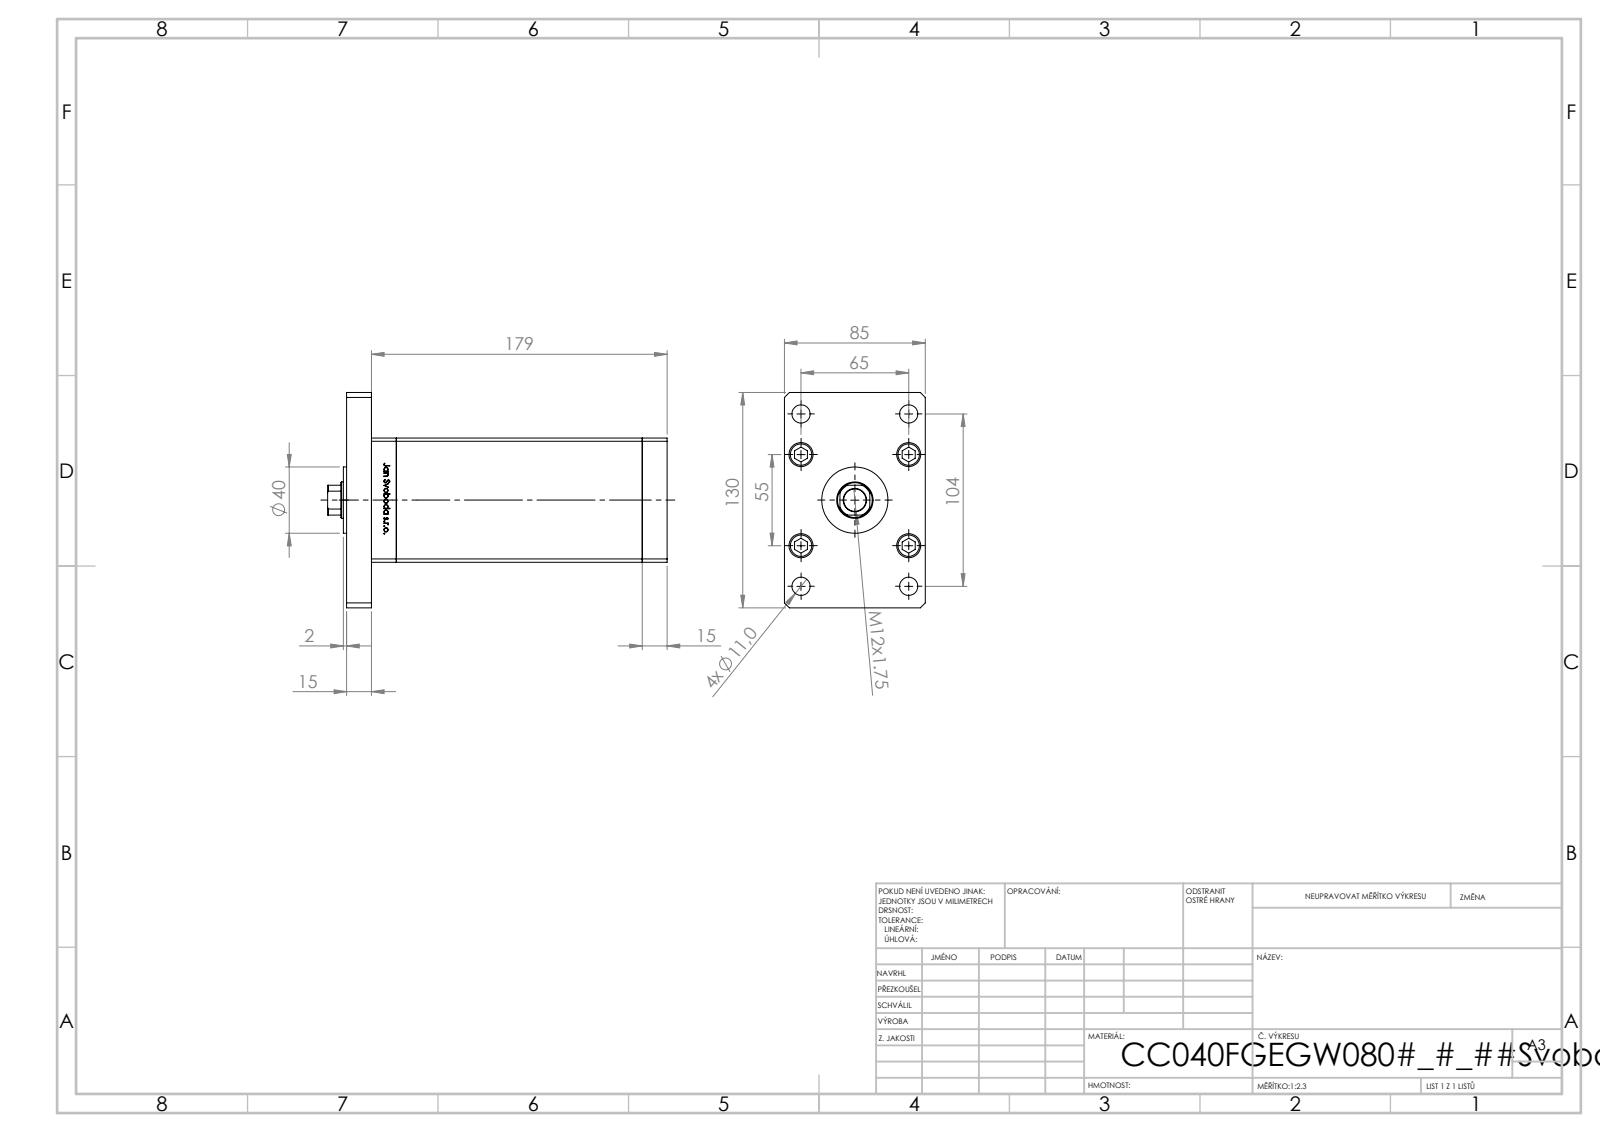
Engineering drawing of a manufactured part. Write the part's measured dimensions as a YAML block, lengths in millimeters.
part_name: "V220C BACK_F; V220C_FRONT_F; V220C_F; V220C_F_MIDDLE (+2 more)"
step_written_by: "SolidWorks 2019 (CONFIG_CONTROL_DESIGN)"
units: millimeters
bodies: {solids: 19, faces: 1310, planar: 517, cylindrical: 187, other: 606}
overall_size: [205, 130, 85]
volume: 1165000
surface_area: 198888
round_holes:
  - {diameter: 11, count: 9}
  - {diameter: 15.5, count: 5}
  - {diameter: 10, count: 4}
  - {diameter: 14.5, count: 4}
  - {diameter: 2, count: 2}
  - {diameter: 13.16, count: 2}
  - {diameter: 13.5, count: 1}
  - {diameter: 22, count: 1}
  - {diameter: 23.5, count: 1}
round_bosses_or_shafts:
  - {diameter: 8, count: 9}
  - {diameter: 14.5, count: 5}
  - {diameter: 40, count: 1}
partial_cylinders:
  - {radius: 0.93, count: 2}
  - {radius: 10.5, count: 1}
face_to_face_distances: [15, 85, 163.5, 178.5, 75, 30, 148.5, 193.5, 10.5, 27.5]
hole_center_spacings: [28, 24.5, 42.57, 61.32, 65, 69.46, 79.5, 102.69]
